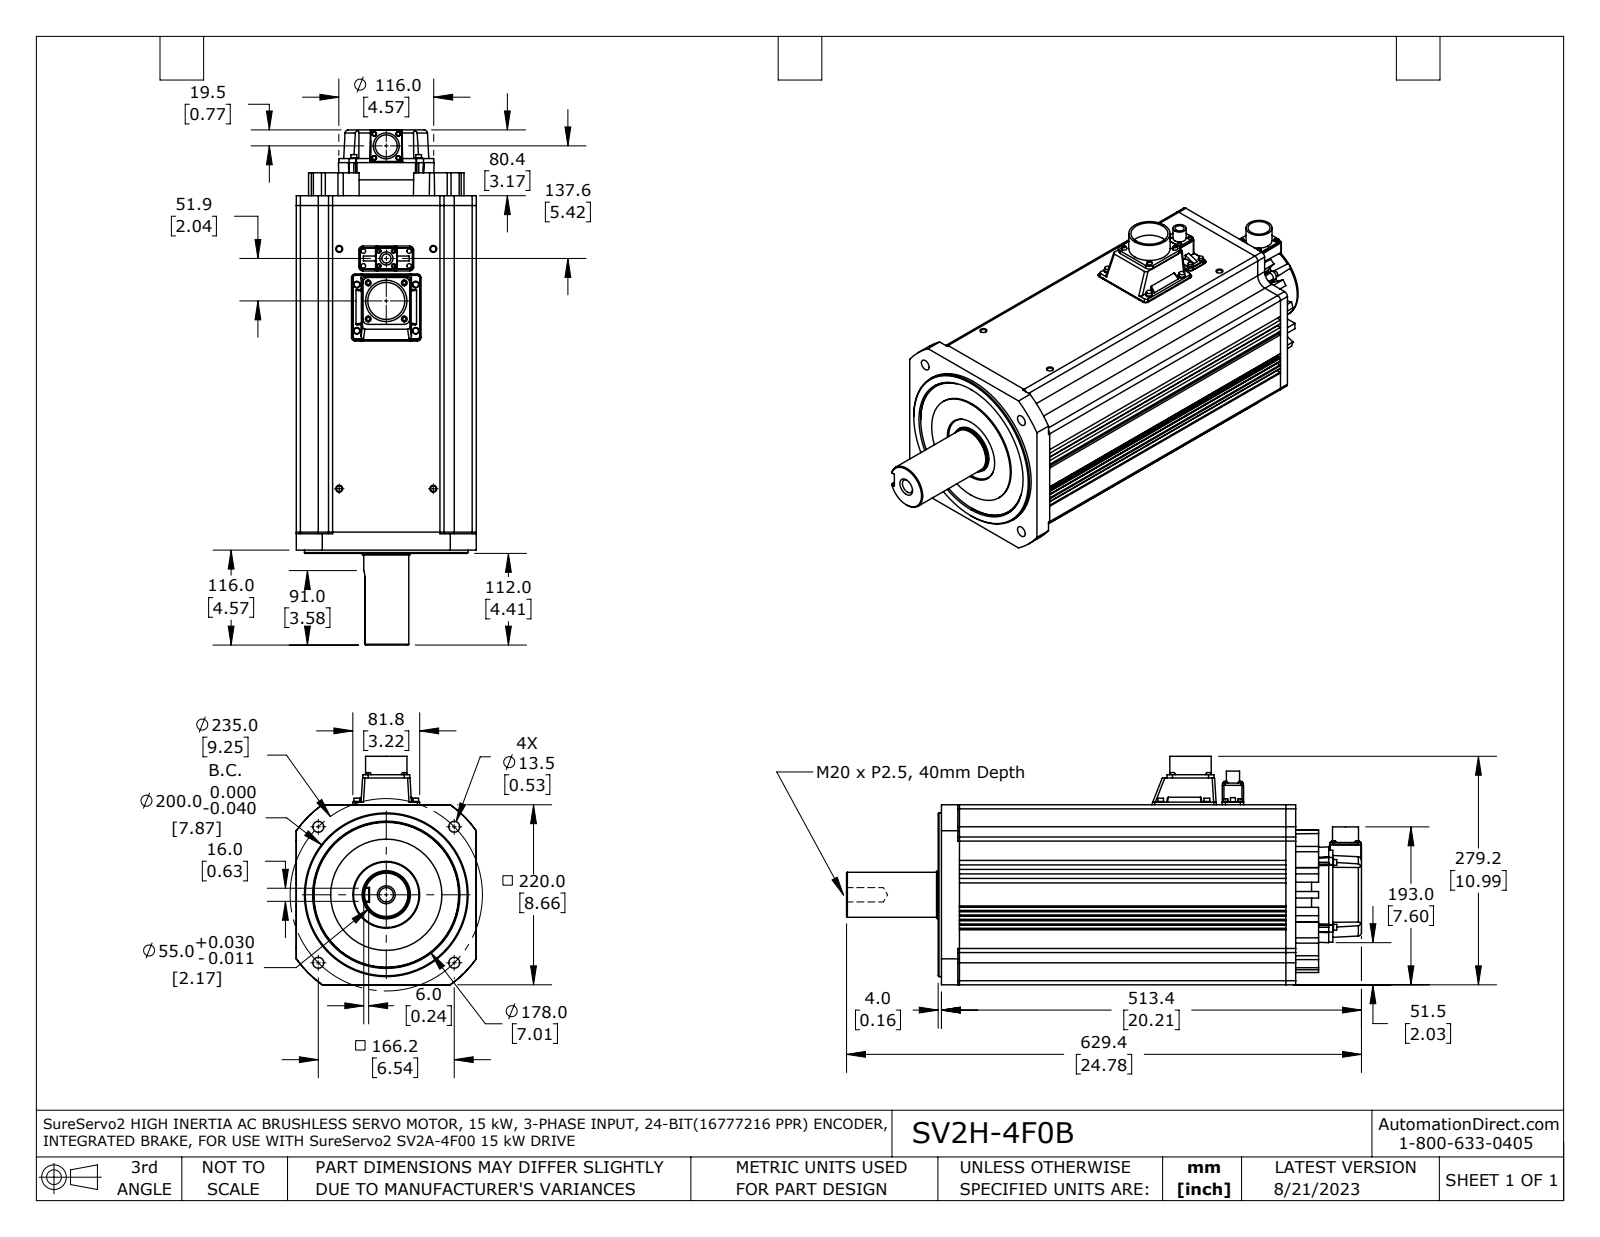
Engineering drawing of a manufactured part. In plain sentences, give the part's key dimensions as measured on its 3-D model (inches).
The part is named "SV2H-4F0B cut1b fxt". Its 3-D file was written by "SolidWorks 2021 (AUTOMOTIVE_DESIGN)". It is 1 solid with 825 faces: 392 planar, 288 cylindrical and 145 other. Overall it measures 24.78 by 10.992 by 8.661 inches. Its volume is 1 196 cubic inches and its surface area 1 050 square inches. Round holes: 4 of diameter 0.169, 4 of diameter 0.181, 4 of diameter 0.268, 4 of diameter 0.531, 1 of diameter 0.437, 1 of diameter 0.689, 1 of diameter 1.058, 1 of diameter 1.783, 1 of diameter 7.087. Round bosses or shafts: 8 of diameter 0.315, 8 of diameter 0.276, 4 of diameter 0.236, 4 of diameter 0.217, 4 of diameter 0.157, 1 of diameter 7.874, 1 of diameter 7.008, 1 of diameter 5.354. Partial cylindrical surfaces (rounded edges, fillets, slot ends): 28 of radius 0.197, 24 of radius 0.031, 20 of radius 0.02, 20 of radius 0.118, 16 of radius 0.157, 8 of radius 0.118, 4 of radius 0.039, 4 of radius 0.079. The main face-to-face distances are 8.661, 1.551, 7.11, 0.217, 0.433, 5.559, 2.441, 2.657, 0.65, 2.224. The hole center spacings are 4.626, 6.543, 1.621, 1.912, 2.019, 2.224, 2.835, 3.374.
